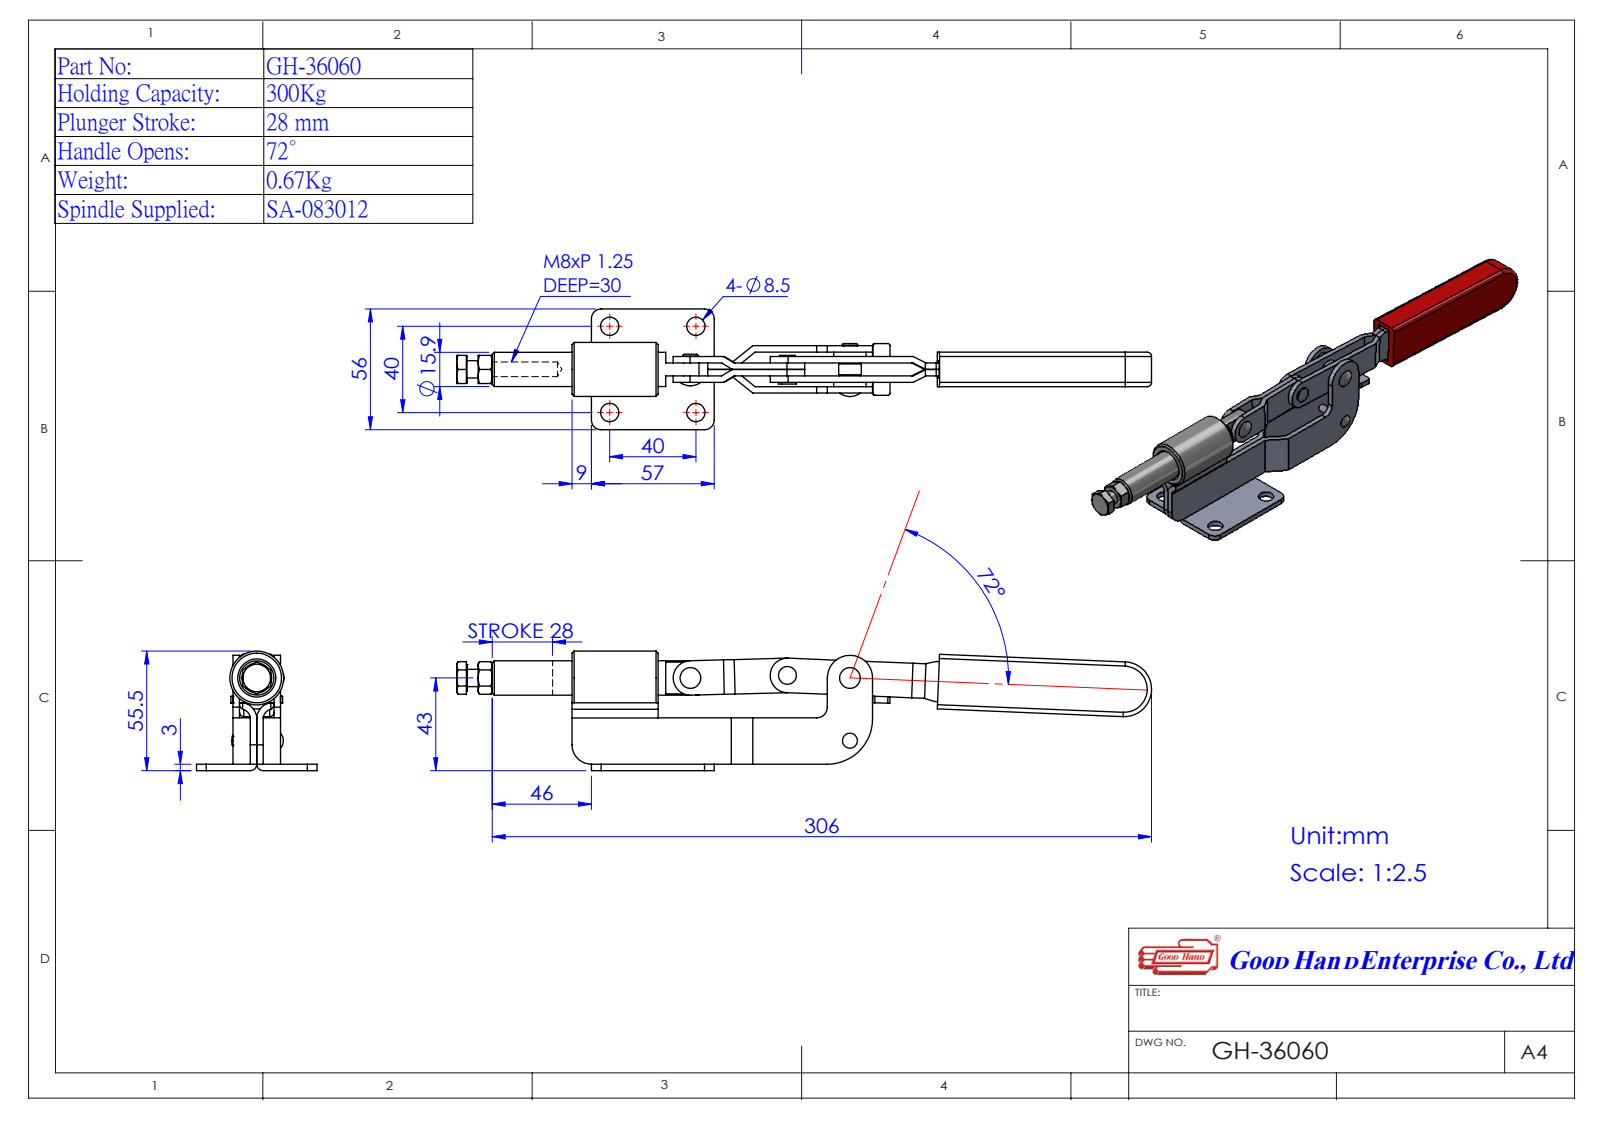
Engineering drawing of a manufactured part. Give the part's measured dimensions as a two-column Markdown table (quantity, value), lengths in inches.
| quantity | value |
| --- | --- |
| part name | 4300732-1^GH-36060(簡化); Group2^GH-36060(簡化); Group3^GH-36060(簡化); Group5^GH-36060(簡化) (+2 more) |
| STEP written by | SolidWorks 2016 (AUTOMOTIVE_DESIGN) |
| units | inches |
| bodies | 6 solids, 245 faces (120 planar, 87 cylindrical, 38 other) |
| overall size | 12.697 × 2.205 × 2.185 |
| volume | 7.094 in³ |
| surface area | 81.59 in² |
| round holes (diameter × count) | 0.335 × 4, 0.197 × 3, 0.268 × 1, 0.626 × 1 |
| round bosses / shafts (diameter × count) | 0.287 × 2, 0.984 × 1, 0.63 × 1, 0.591 × 1, 0.492 × 1, 0.315 × 1, 0.256 × 1, 0.248 × 1 |
| partial cylindrical surfaces (radius × count) | 0.177 × 6, 0.039 × 4, 0.079 × 4, 0.118 × 2, 0.295 × 2, 0.197 × 1, 0.315 × 1, 0.354 × 1 |
| main face-to-face distances | 0.197, 0.433, 0.118, 0.236, 0.63, 0.354, 0.079, 0.551, 0.748, 0.117 |
| hole center spacings | 1.575, 2.227, 1.143, 1.773, 2.915 |
